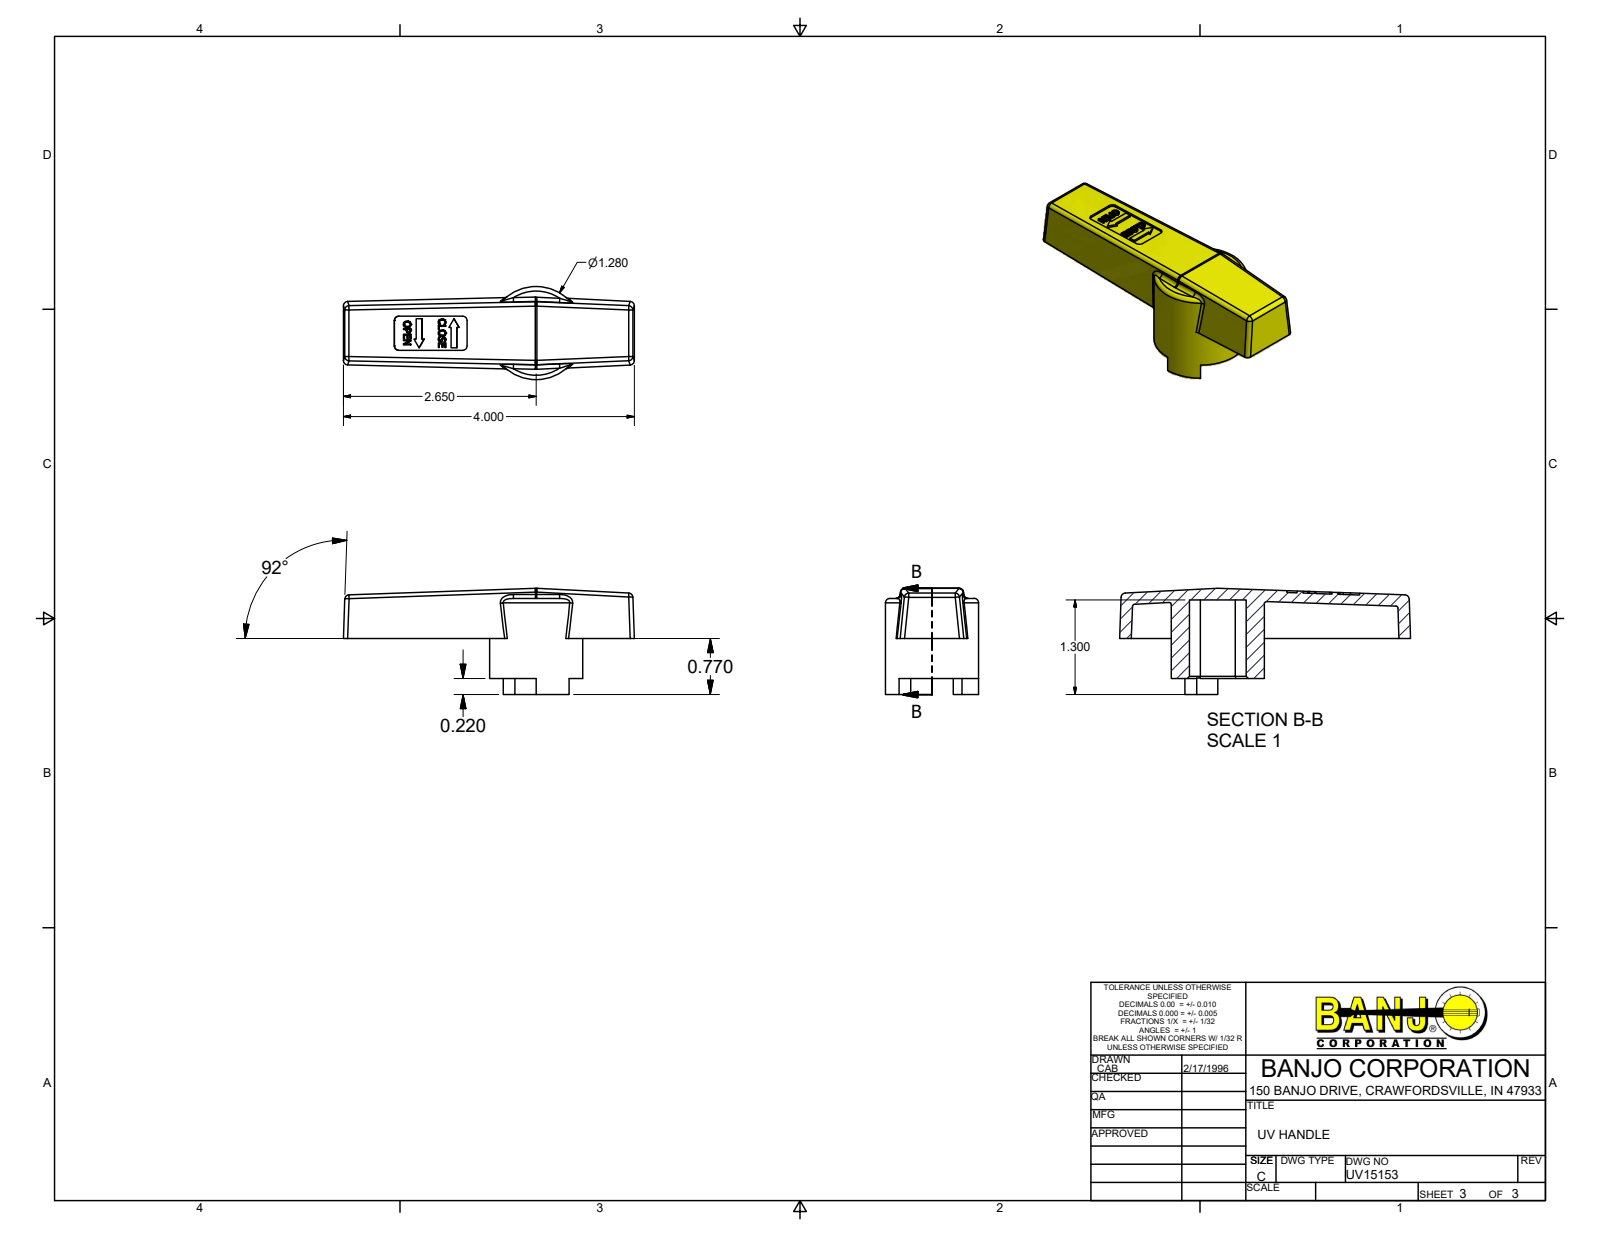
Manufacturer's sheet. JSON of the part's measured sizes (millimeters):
{"part_name": "UV15153", "step_written_by": "Autodesk Inventor 2017 (AUTOMOTIVE_DESIGN)", "units": "millimeters", "bodies": {"solids": 1, "faces": 264, "planar": 122, "cylindrical": 36, "other": 106}, "overall_size": [101.6, 37.08, 32.51], "volume_mm3": 32677, "surface_area_mm2": 14110, "round_bosses_or_shafts": [[32.51, 1]], "partial_cylinders_radius": [[1.52, 18], [0.76, 10], [6.35, 3], [9.91, 1], [10.48, 1]], "face_to_face_distances": [4.06, 4.07, 13.97, 15.62, 27.43, 13.46, 3.43, 0.63, 5.59, 19.56]}
